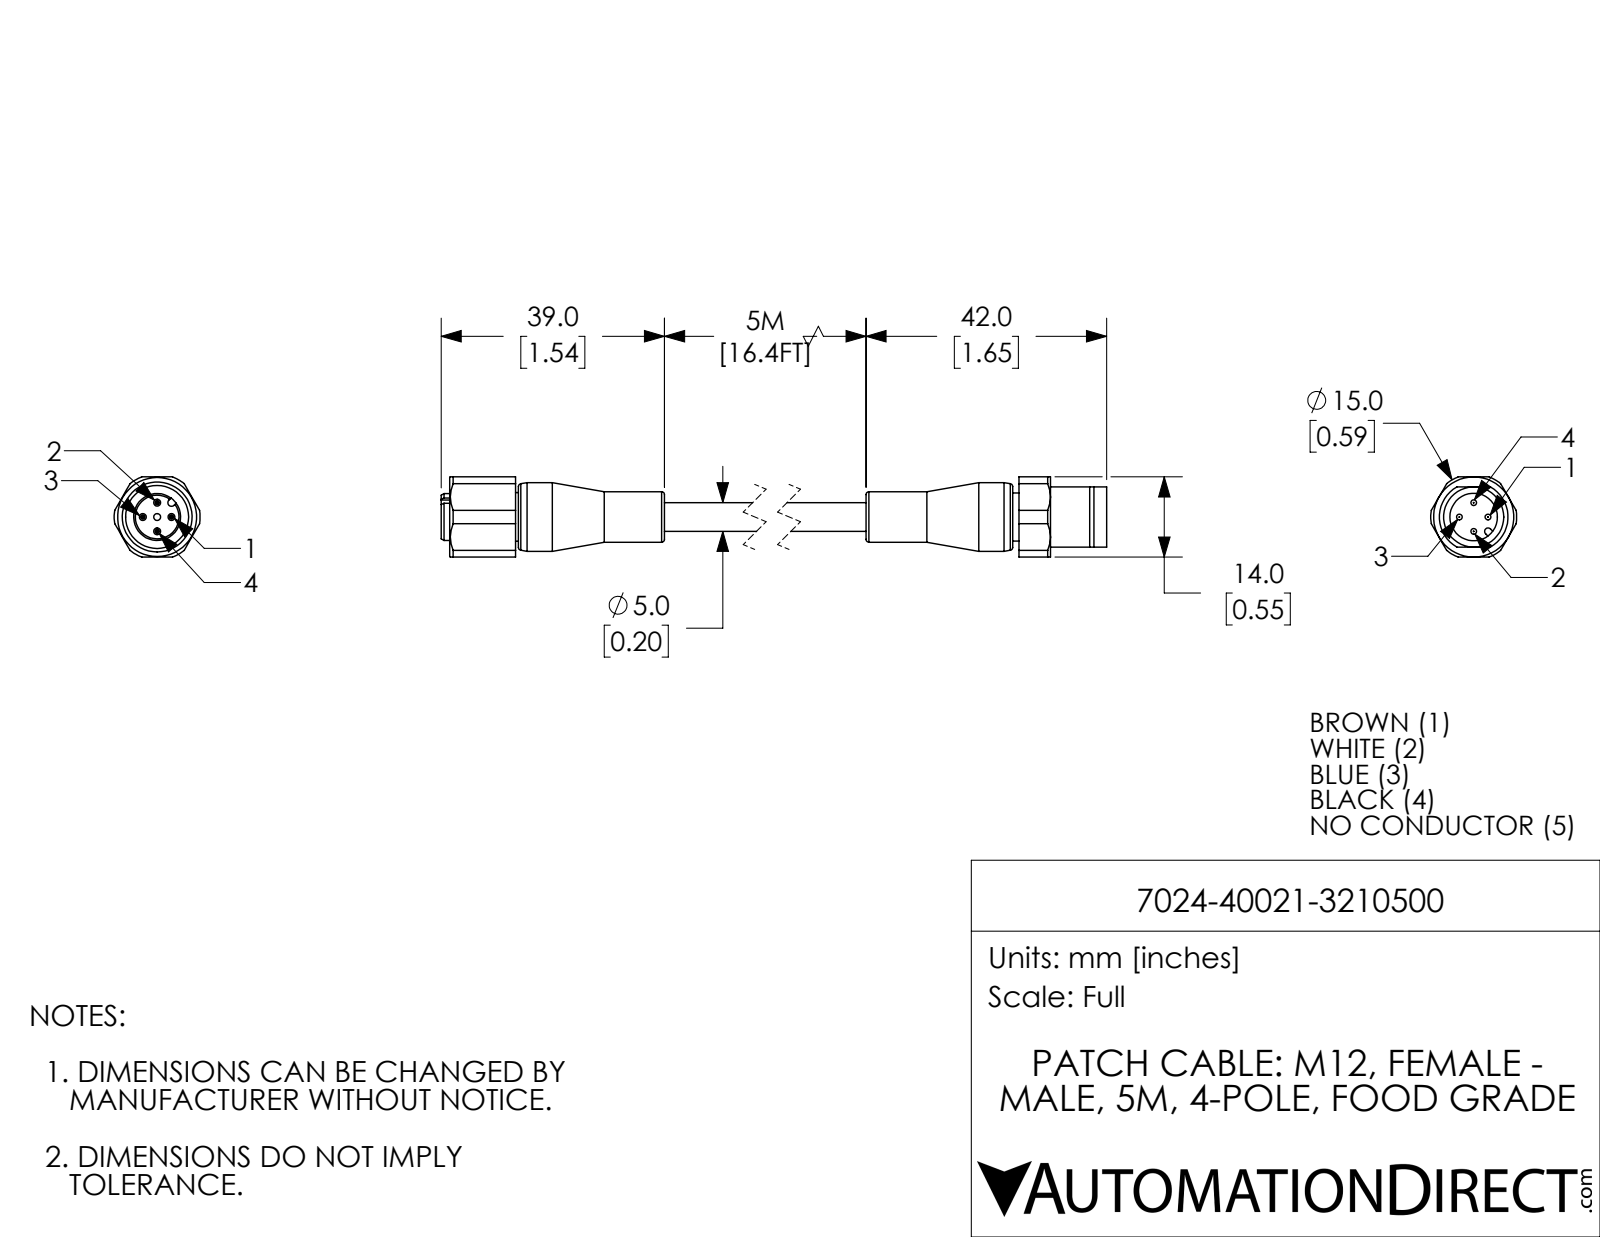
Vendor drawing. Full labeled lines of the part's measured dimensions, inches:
Part name (STEP PRODUCT): 7024-40021-3210500; 7024-40021-3210500_MALE; 7024-40021-3210500_FEMALE
STEP written by: SolidWorks 2018 (AUTOMOTIVE_DESIGN)
Units: inches
Bodies: 2 solids, 144 faces (43 planar, 60 cylindrical, 41 other)
Overall size (bounding box): 5.165 × 0.591 × 0.551
Volume: 0.491 in³ · Surface area: 7.86 in²
Round holes (diameter × count): ⌀0.047 ×5, ⌀0.327 ×1, ⌀0.433 ×1
Round bosses / shafts (diameter × count): ⌀0.039 ×4, ⌀0.472 ×1, ⌀0.413 ×1, ⌀0.346 ×1, ⌀0.335 ×1, ⌀0.331 ×1, ⌀0.323 ×1, ⌀0.197 ×1
Partial cylindrical surfaces — rounded edges, fillets, slot ends (radius × count): R0.024 ×1, R0.026 ×1, R0.295 ×1
Main face-to-face distances: 0.551, 4.051, 0.069, 0.482, 4.461, 0.295, 0.217, 4.303, 0.252, 4.268
Hole centre spacings: 0.098, 0.139, 0.197
